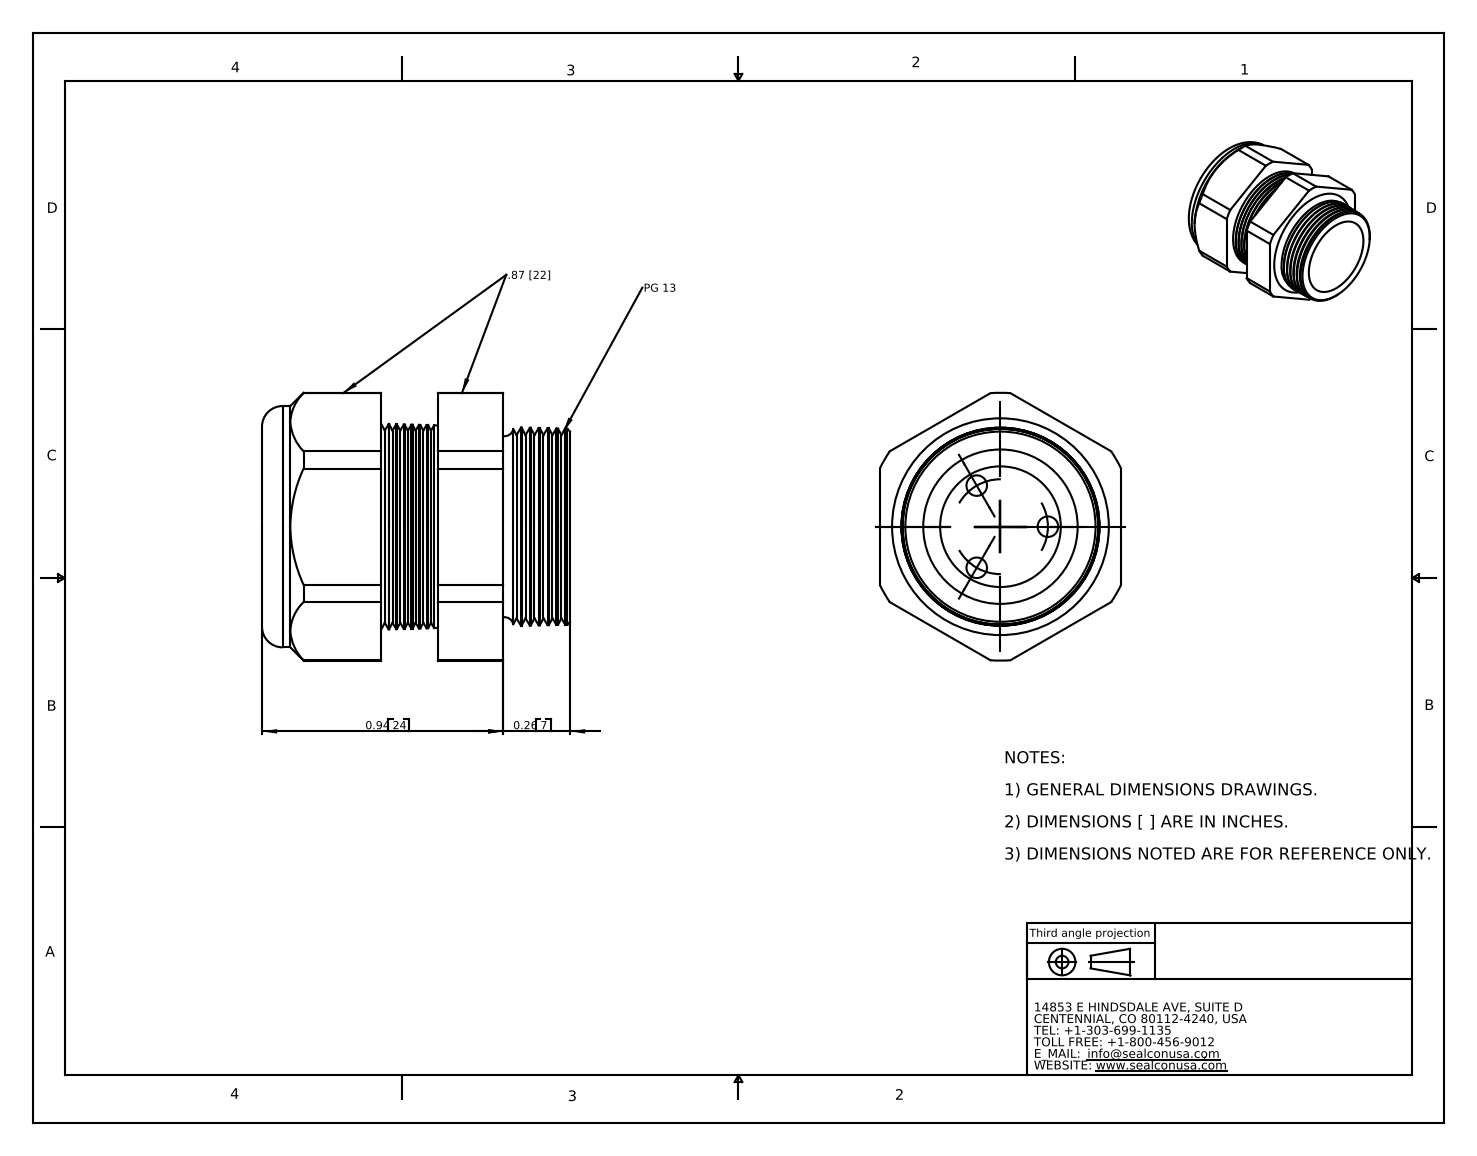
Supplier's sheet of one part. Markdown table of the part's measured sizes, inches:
| quantity | value |
| --- | --- |
| part name | CD13A1-BR |
| STEP written by | SolidWorks 2007 (CONFIG_CONTROL_DESIGN) |
| units | inches |
| bodies | 2 solids, 140 faces (20 planar, 26 cylindrical, 94 other) |
| overall size | 1.2 × 1.043 × 0.94 |
| volume | 0.537 in³ |
| surface area | 8.691 in² |
| round holes (diameter × count) | 0.08 × 3, 0.45 × 1, 0.47 × 1 |
| round bosses / shafts (diameter × count) | 0.94 × 1 |
| partial cylindrical surfaces (radius × count) | 0.522 × 1 |
| main face-to-face distances | 0.94, 0.684, 0.465, 0.22, 0.476, 0.256, 0.25, 0.215, 0.434, 0.69 |
| hole center spacings | 0.185, 0.32, 0.185, 0.32 |
